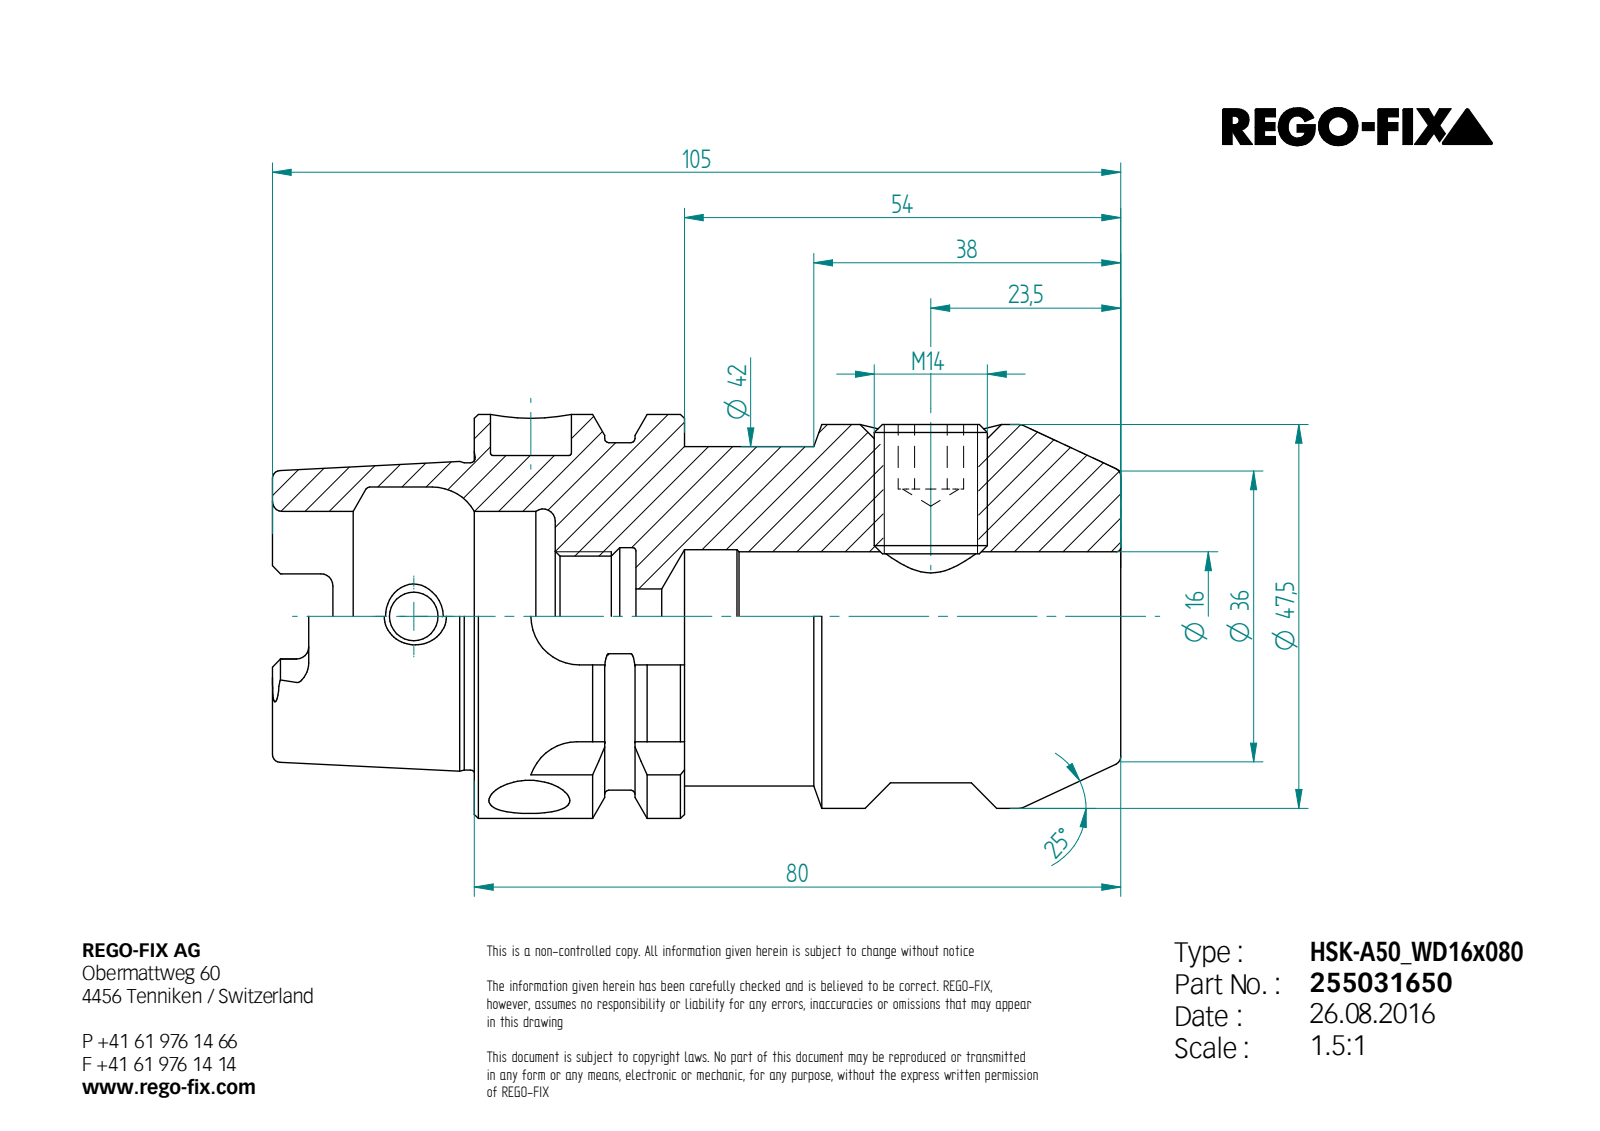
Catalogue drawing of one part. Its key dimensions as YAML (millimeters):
step_written_by: "Unknown (AUTOMOTIVE_DESIGN)"
units: millimeters
bodies: {solids: 2, faces: 155, planar: 64, cylindrical: 37, other: 54}
overall_size: [105, 50, 50]
volume: 121328
surface_area: 27018
round_holes:
  - {diameter: 10, count: 2}
  - {diameter: 6, count: 1}
  - {diameter: 6.8, count: 1}
  - {diameter: 11.84, count: 1}
  - {diameter: 14.92, count: 1}
  - {diameter: 16, count: 1}
  - {diameter: 16.5, count: 1}
  - {diameter: 17, count: 1}
  - {diameter: 26, count: 1}
  - {diameter: 32, count: 1}
round_bosses_or_shafts:
  - {diameter: 50, count: 1}
  - {diameter: 47.5, count: 1}
  - {diameter: 43, count: 1}
  - {diameter: 42, count: 1}
  - {diameter: 38.01, count: 1}
  - {diameter: 14, count: 1}
partial_cylinders:
  - {radius: 1.5, count: 6}
  - {radius: 2.38, count: 4}
  - {radius: 6, count: 4}
face_to_face_distances: [80, 26, 54, 10, 16, 70, 42, 25, 35, 51]
hole_center_spacings: [49.5]
